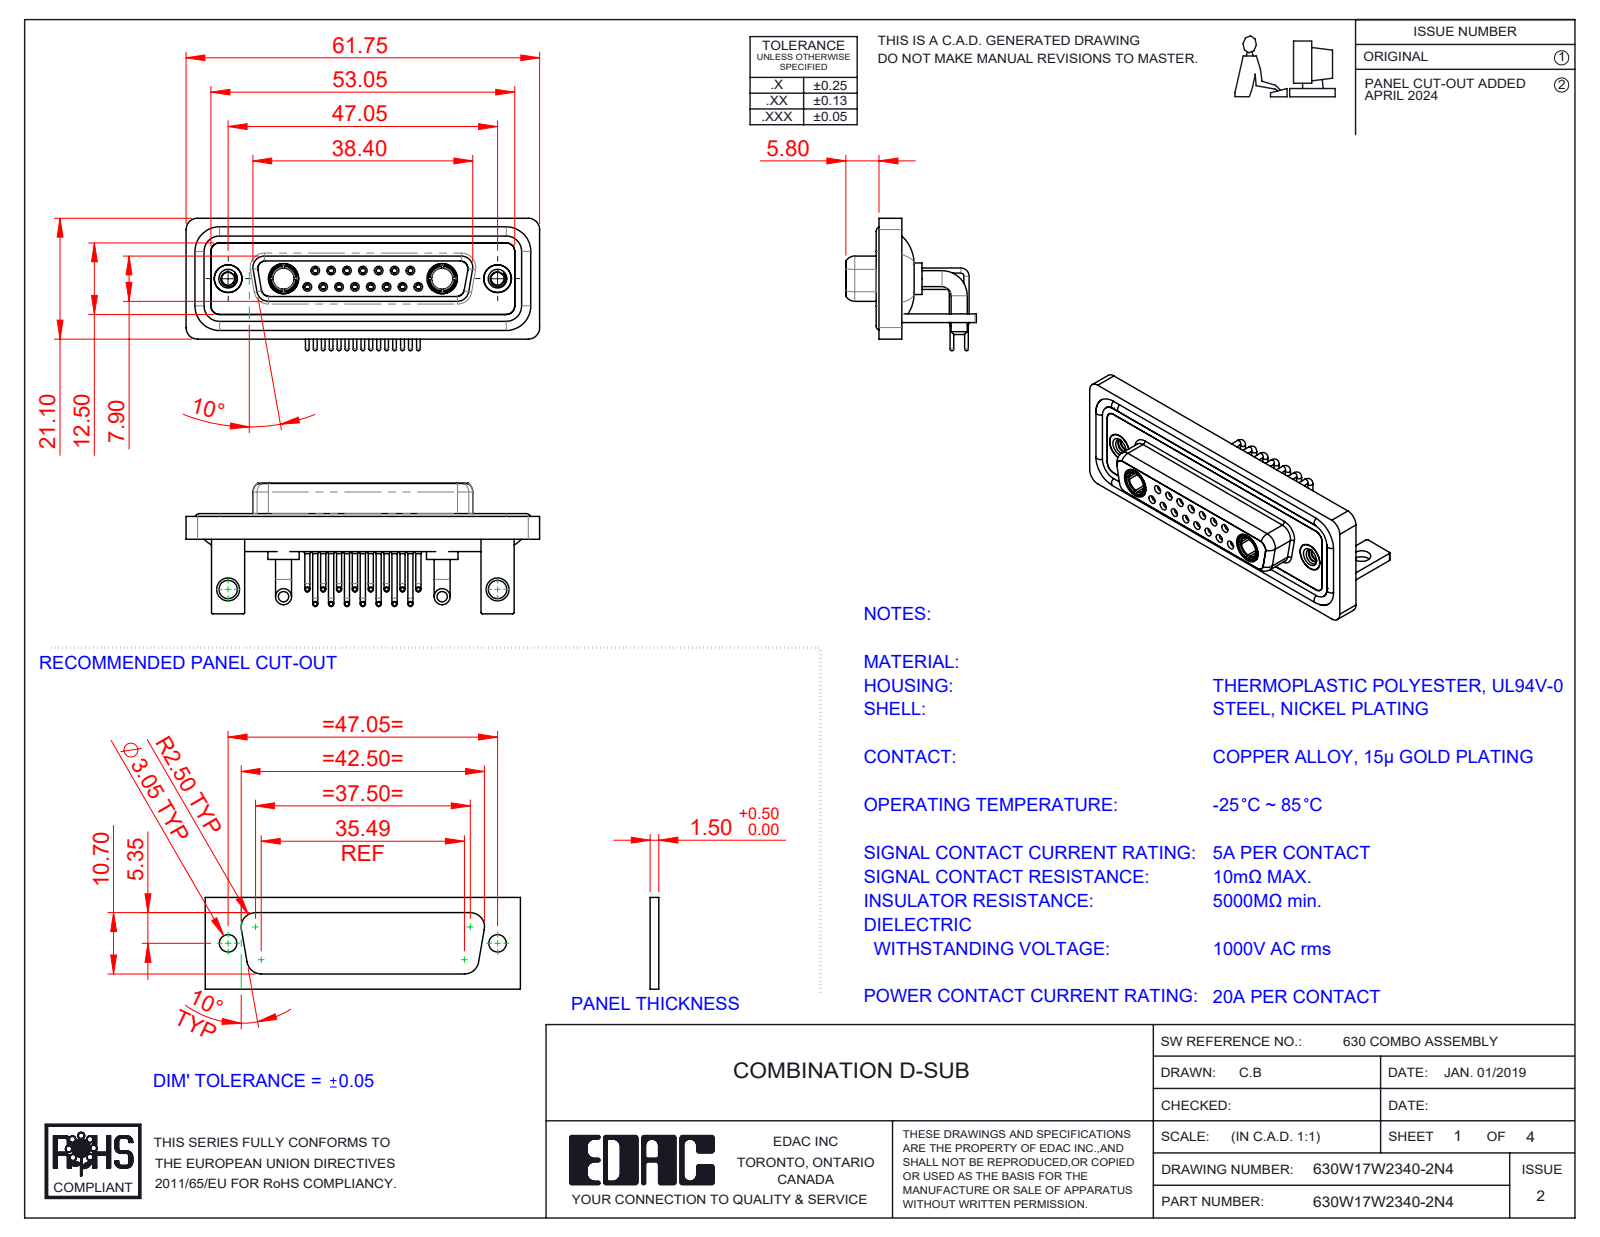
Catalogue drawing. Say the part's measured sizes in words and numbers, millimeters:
The part is named "630Combo Waterproof Housing_25 Contacts; 630Combo Stabilizer Bracket_50 Contacts; 630Combo Threaded Rivet_2; 630Combo Shell Front_25 Contacts (+6 more)". Its 3-D file was written by "SolidWorks 2023 (CONFIG_CONTROL_DESIGN)". It is 28 solids with 1385 faces: 408 planar, 607 cylindrical and 370 other. Overall it measures 61.75 by 23.12 by 22.8 millimeters. Its volume is 8 853 cubic millimeters and its surface area 15 266 square millimeters. Round holes: 15 of diameter 0.9, 15 of diameter 1.1, 15 of diameter 1.5, 15 of diameter 2, 8 of diameter 1.6, 7 of diameter 1.7, 4 of diameter 4.85, 2 of diameter 2.26, 2 of diameter 3.2, 2 of diameter 3.7, 2 of diameter 4, 2 of diameter 4.05. Round bosses or shafts: 15 of diameter 0.9, 15 of diameter 0.65, 11 of diameter 1.6, 4 of diameter 2.8, 2 of diameter 5.5, 2 of diameter 5.2, 2 of diameter 4.96, 2 of diameter 4.95. Partial cylindrical surfaces (rounded edges, fillets, slot ends): 19 of radius 2, 18 of radius 1.5, 16 of radius 0.25, 8 of radius 1.35, 8 of radius 1.6, 5 of radius 0.5, 4 of radius 0.6, 4 of radius 0.65. The main face-to-face distances are 0.4, 1.8, 2.9, 3.7, 1.5, 4.1, 1.1, 1.4, 1.6, 3.1. The hole center spacings are 3.16, 2.77, 5.54, 8.31, 5.04, 7.49, 11.08, 5.03.
